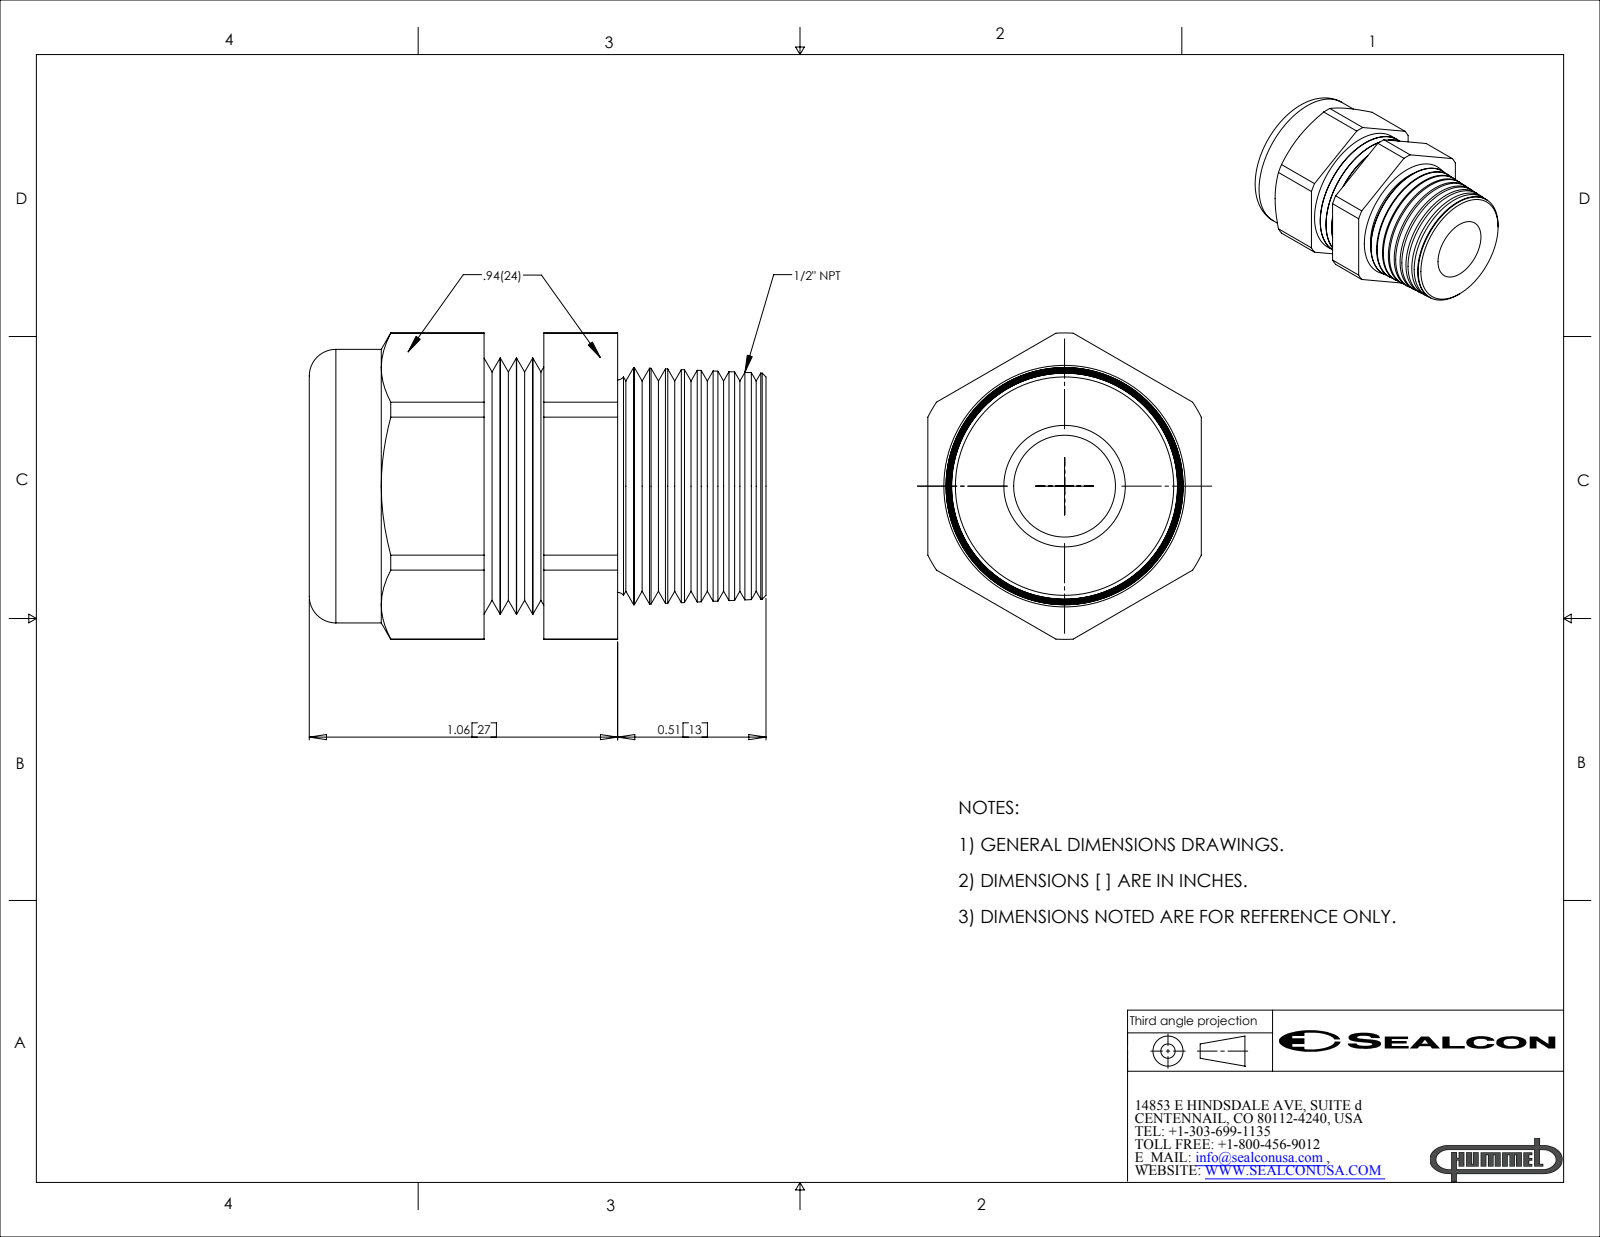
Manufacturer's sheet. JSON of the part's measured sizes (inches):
{"part_name": "CD13NR-BK", "step_written_by": "SolidWorks 2007 (CONFIG_CONTROL_DESIGN)", "units": "inches", "bodies": {"solids": 2, "faces": 138, "planar": 20, "cylindrical": 30, "other": 88}, "overall_size": [1.57, 1.053, 0.94], "volume_in3": 0.796, "surface_area_in2": 10.97, "round_holes": [[0.35, 1], [0.697, 1]], "round_bosses_or_shafts": [[0.94, 1], [0.88, 1]], "partial_cylinders_radius": [[0.526, 1]], "face_to_face_distances": [0.94, 1.322, 0.228, 1.55, 1.04, 0.813, 0.51, 0.787, 0.559, 0.254]}
